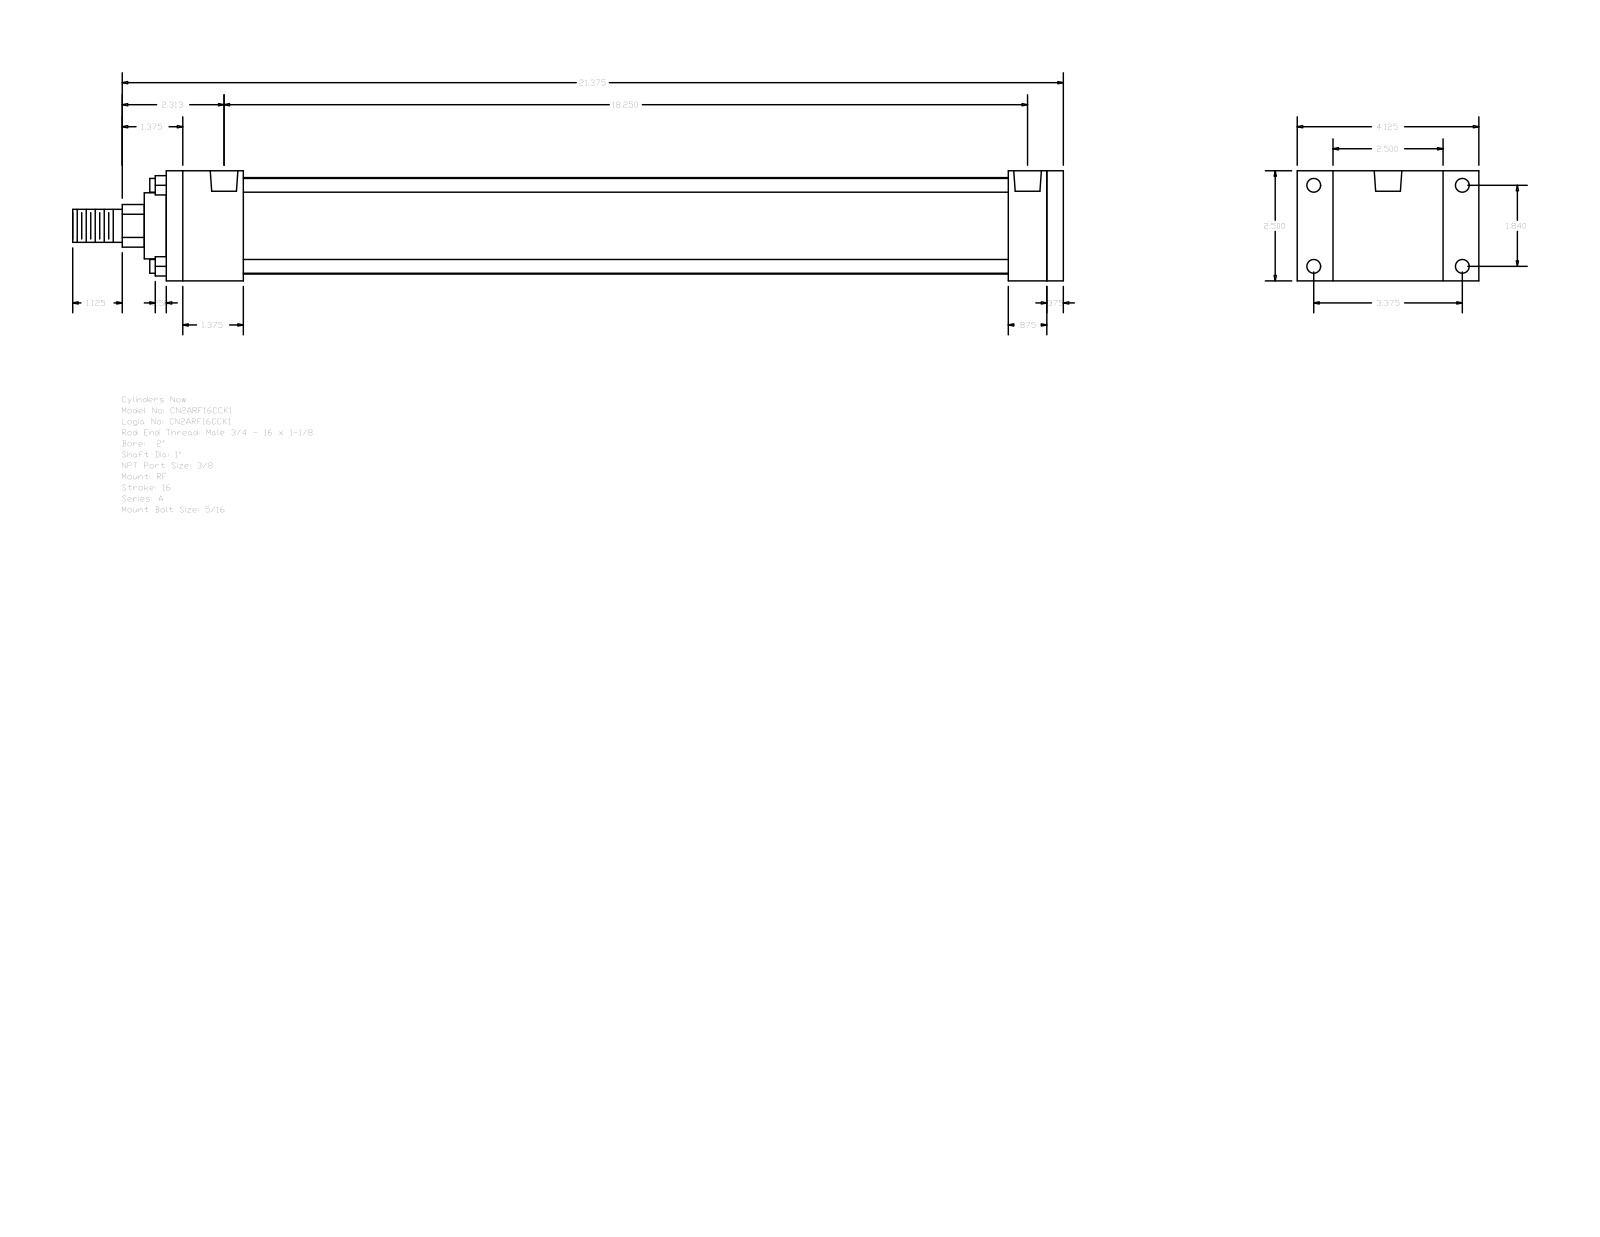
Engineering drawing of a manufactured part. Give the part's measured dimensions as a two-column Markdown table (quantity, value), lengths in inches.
| quantity | value |
| --- | --- |
| part name | A_RF__0200_1 |
| STEP written by | GSSL Pune (CONFIG_CONTROL_DESIGN) |
| units | inches |
| bodies | 0 solids, 92 faces (64 planar, 28 cylindrical, 0 other) |
| overall size | 22.5 × 4.125 × 2.5 |
| round holes (diameter × count) | 0.219 × 4, 0.313 × 4, 0.627 × 2 |
| round bosses / shafts (diameter × count) | 0.313 × 4, 2.19 × 1, 1.5 × 1, 1 × 1, 0.75 × 1 |
| partial cylindrical surfaces (radius × count) | 0.484 × 1 |
| main face-to-face distances | 2.5, 0.375, 20.375, 20, 1.75, 0.813, 18.25, 18.625, 19.125, 17.375 |
| hole center spacings | 1.84, 3.375, 3.844, 18.031, 0.063, 0.157, 18.093, 18.187 |
